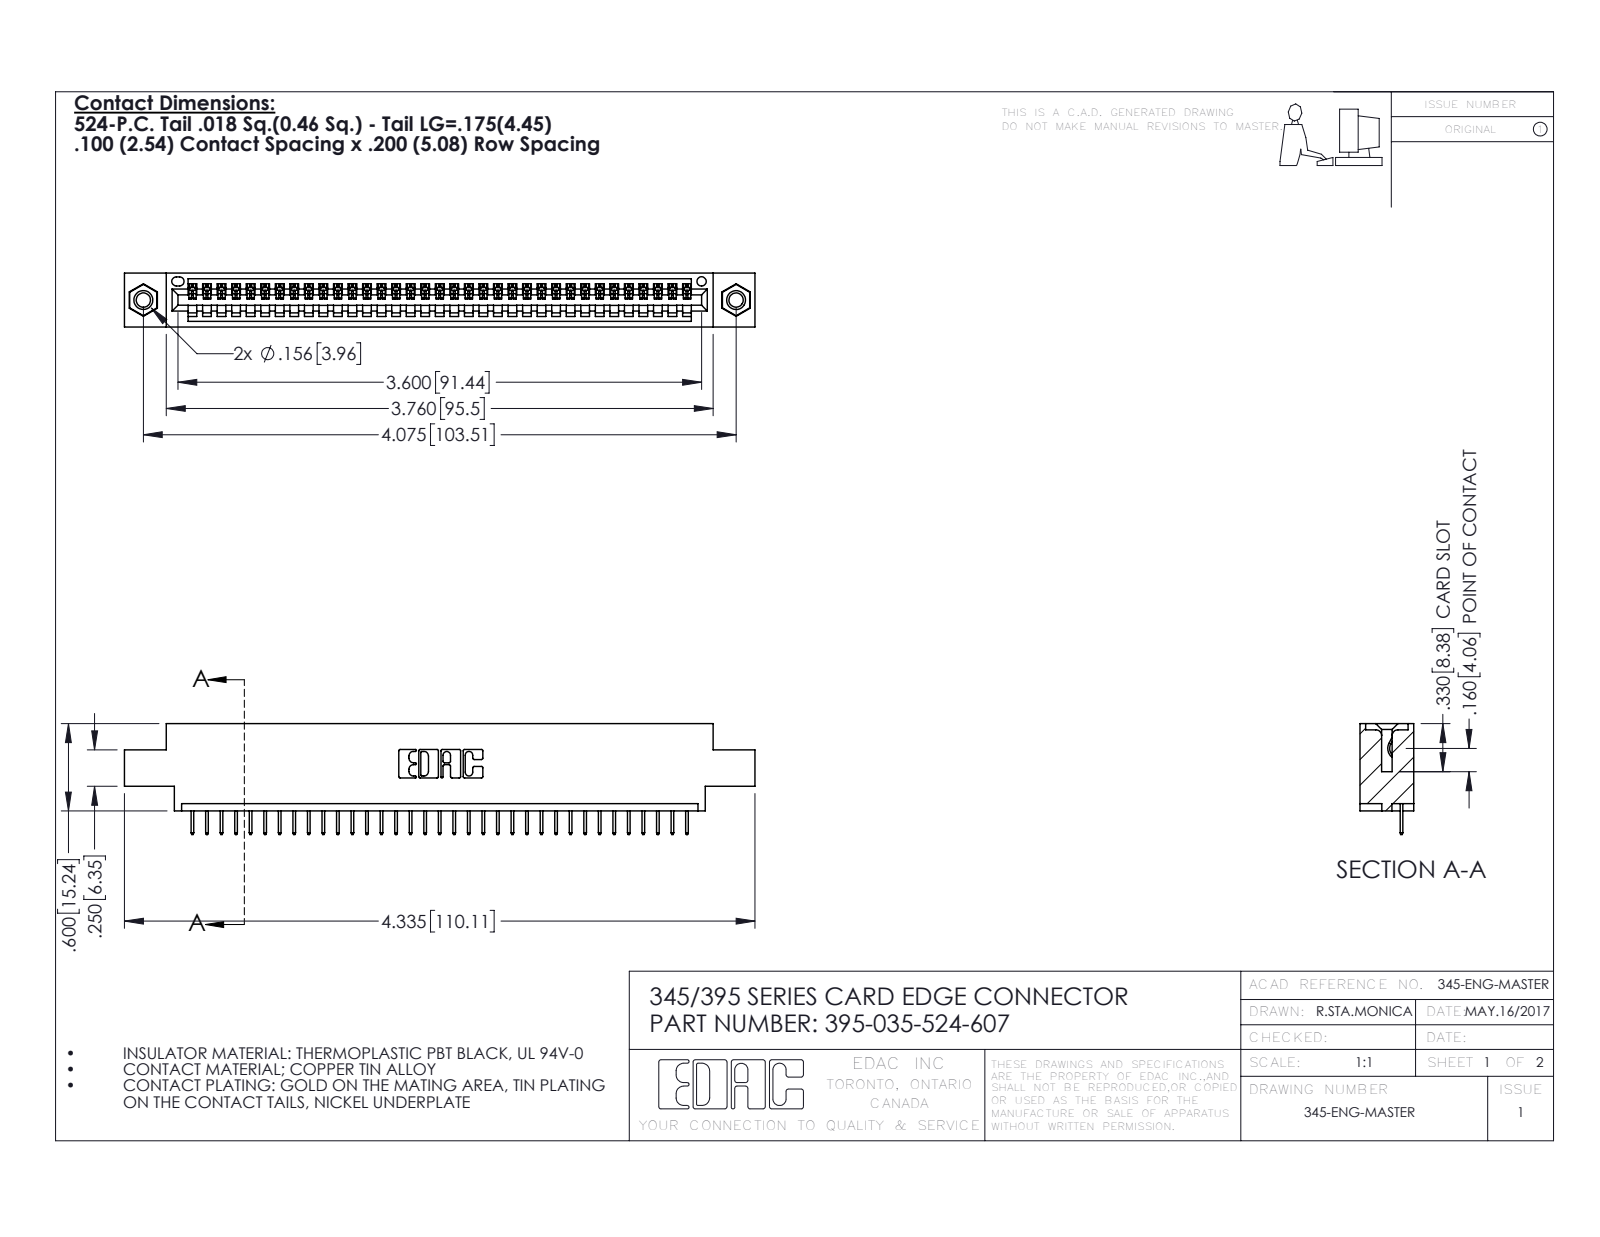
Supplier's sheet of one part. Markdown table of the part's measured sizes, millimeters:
| quantity | value |
| --- | --- |
| part name | 345 Part_0.170 Offset - 0.156 Dia-TI; 395-035-524-607; 345-250-001_345-250-005-103; 345-292-001_345-293-124 |
| STEP written by | SolidWorks 2016 (CONFIG_CONTROL_DESIGN) |
| units | millimeters |
| bodies | 38 solids, 2360 faces (1726 planar, 618 cylindrical, 16 other) |
| overall size | 110.1 × 19.4 × 9.4 |
| volume | 10 100 mm³ |
| surface area | 13 090 mm² |
| round holes (diameter × count) | 2.5 × 2, 3.2 × 2, 4 × 2, 1.6 × 1 |
| round bosses / shafts (diameter × count) | 3.9 × 2 |
| partial cylindrical surfaces (radius × count) | 0.2 × 70, 0.3 × 22, 0.2 × 6, 0.8 × 6, 0.7 × 3, 0.8 × 2, 1 × 2, 0.4 × 1 |
| main face-to-face distances | 1.8, 7.6, 9.4, 5.1, 2.5, 6.9, 0.6, 5.7, 1.8, 4.4 |
| hole center spacings | 6.9, 97.5, 103.5 |
